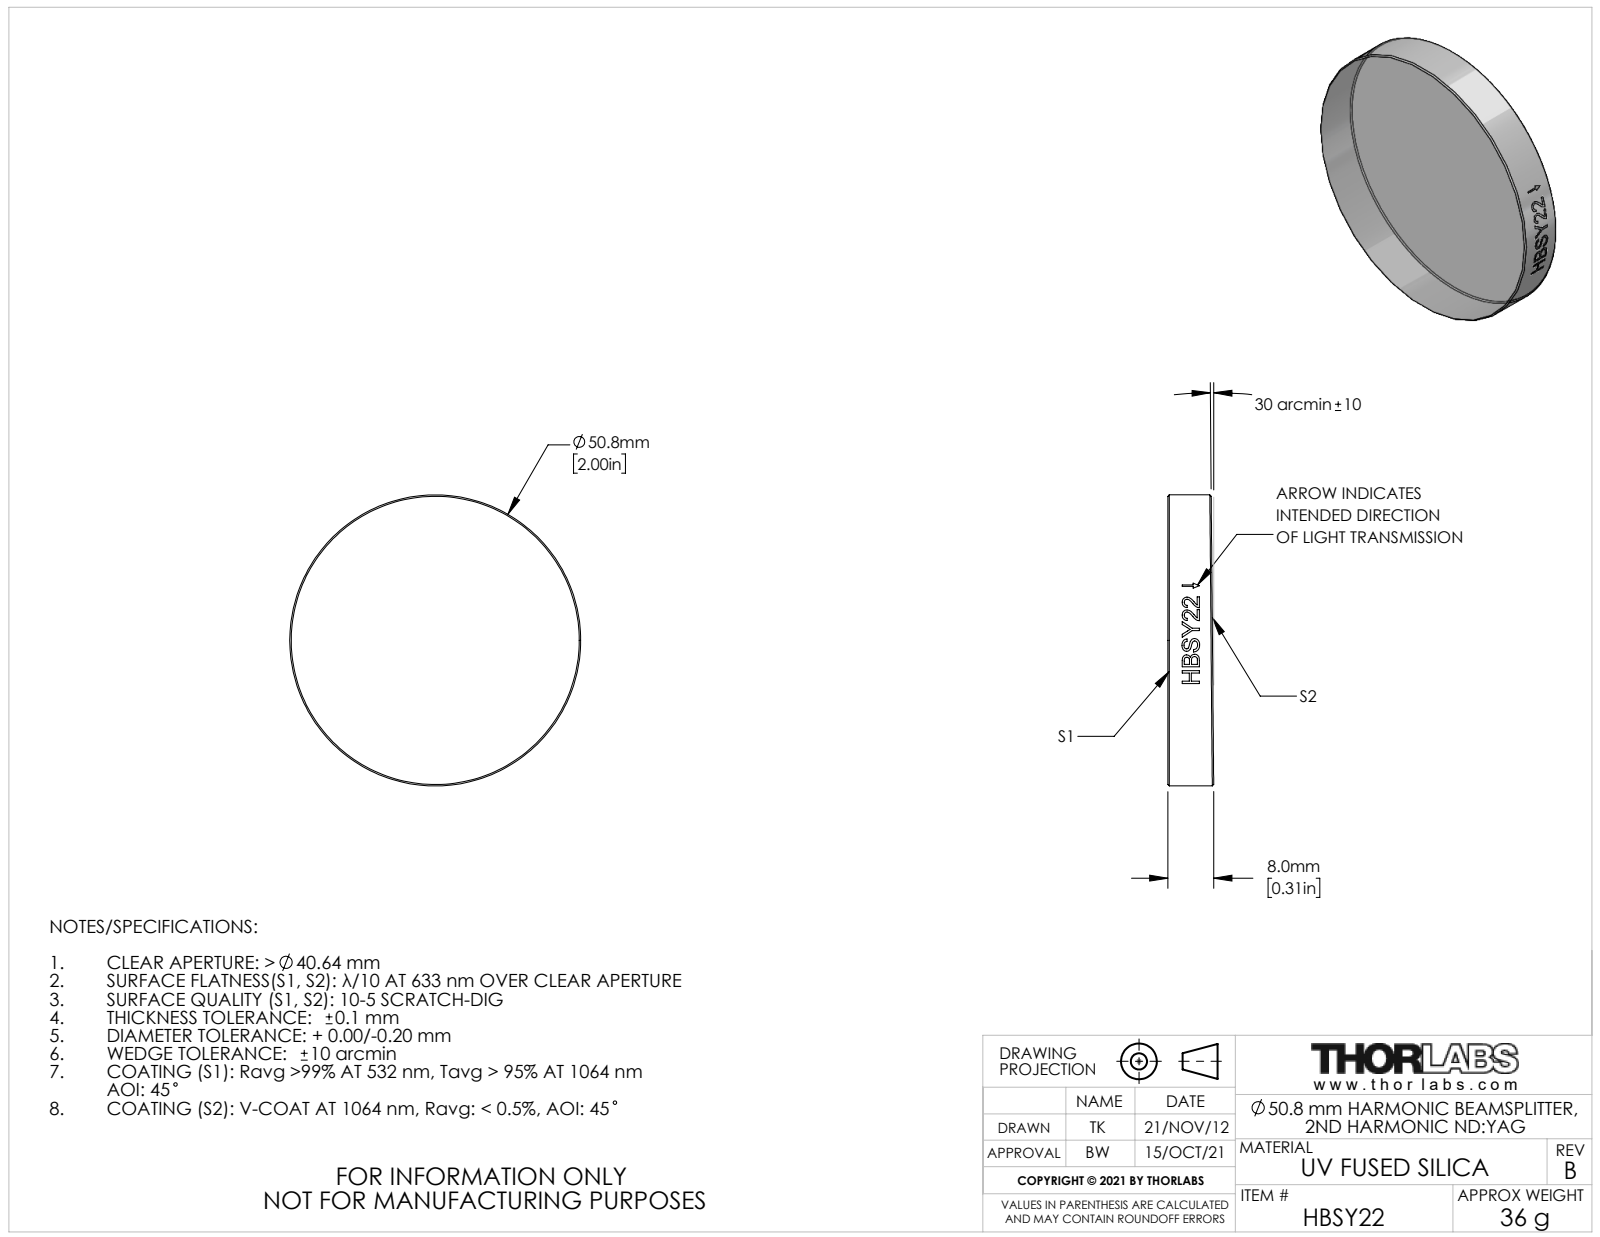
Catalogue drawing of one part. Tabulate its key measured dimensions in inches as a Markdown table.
| quantity | value |
| --- | --- |
| part name | TTN006427-E0W |
| STEP written by | SolidWorks 2012 (CONFIG_CONTROL_DESIGN) |
| units | inches |
| bodies | 1 solid, 18 faces (2 planar, 12 cylindrical, 4 other) |
| overall size | 2 × 2 × 0.315 |
| volume | 0.961 in³ |
| surface area | 8.134 in² |
| round bosses / shafts (diameter × count) | 2 × 1 |
